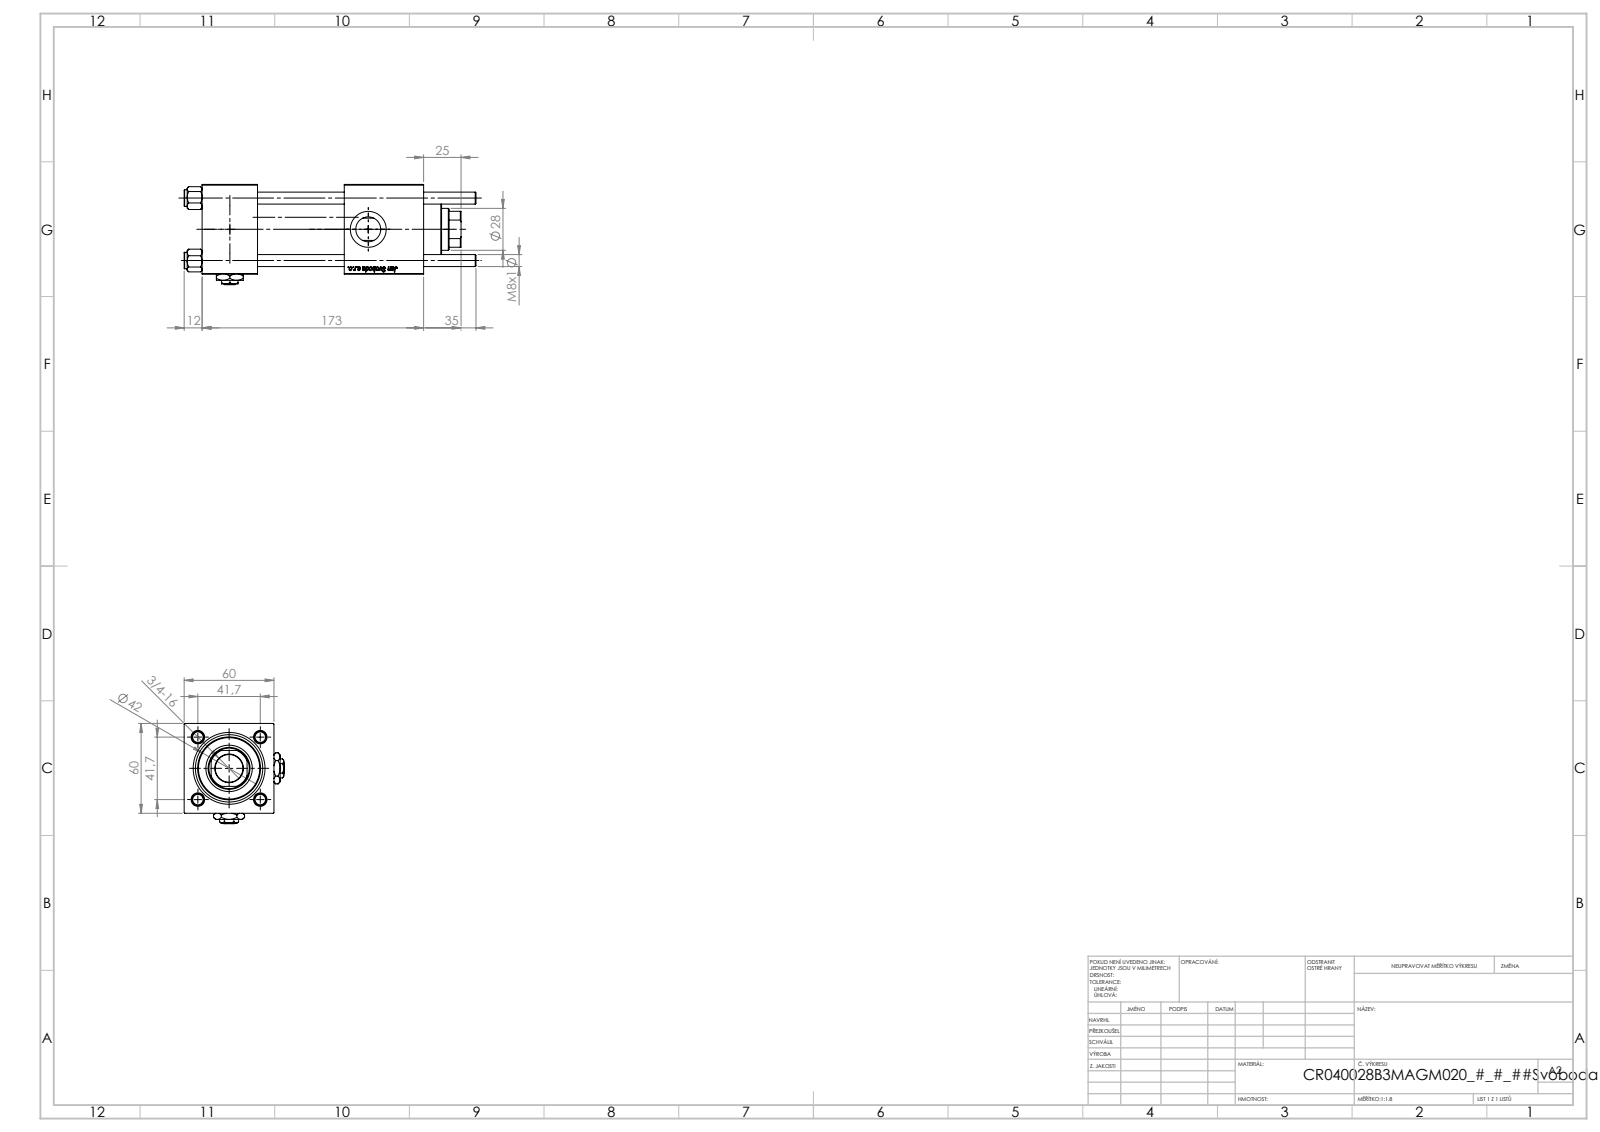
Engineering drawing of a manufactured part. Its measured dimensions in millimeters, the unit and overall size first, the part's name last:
Units: millimetres
Overall size (bounding box): 195 × 67 × 67
Round holes (diameter × count): ⌀8 ×4, ⌀7 ×2, ⌀16.66 ×2, ⌀24 ×2, ⌀16 ×1, ⌀18.5 ×1, ⌀28 ×1, ⌀31 ×1, ⌀40 ×1, ⌀45 ×1
Round bosses / shafts (diameter × count): ⌀11 ×4, ⌀46 ×1, ⌀42 ×1
Partial cylindrical surfaces — rounded edges, fillets, slot ends (radius × count): R13.5 ×1
Main face-to-face distances: 60, 37, 58, 95, 53, 119.3, 82.3, 24.3, 148, 111
Hole centre spacings: 29.49, 41.7, 58.97
Volume: 431 626 mm³ · Surface area: 122 974 mm²
Bodies: 13 solids, 1260 faces (480 planar, 90 cylindrical, 690 other)
Part name (STEP PRODUCT): NUT_M5_B; V215_VC_A; Zatka_pro_OIL_PORT; V215CR_B-1 (+2 more)
STEP written by: SolidWorks 2019 (CONFIG_CONTROL_DESIGN)
